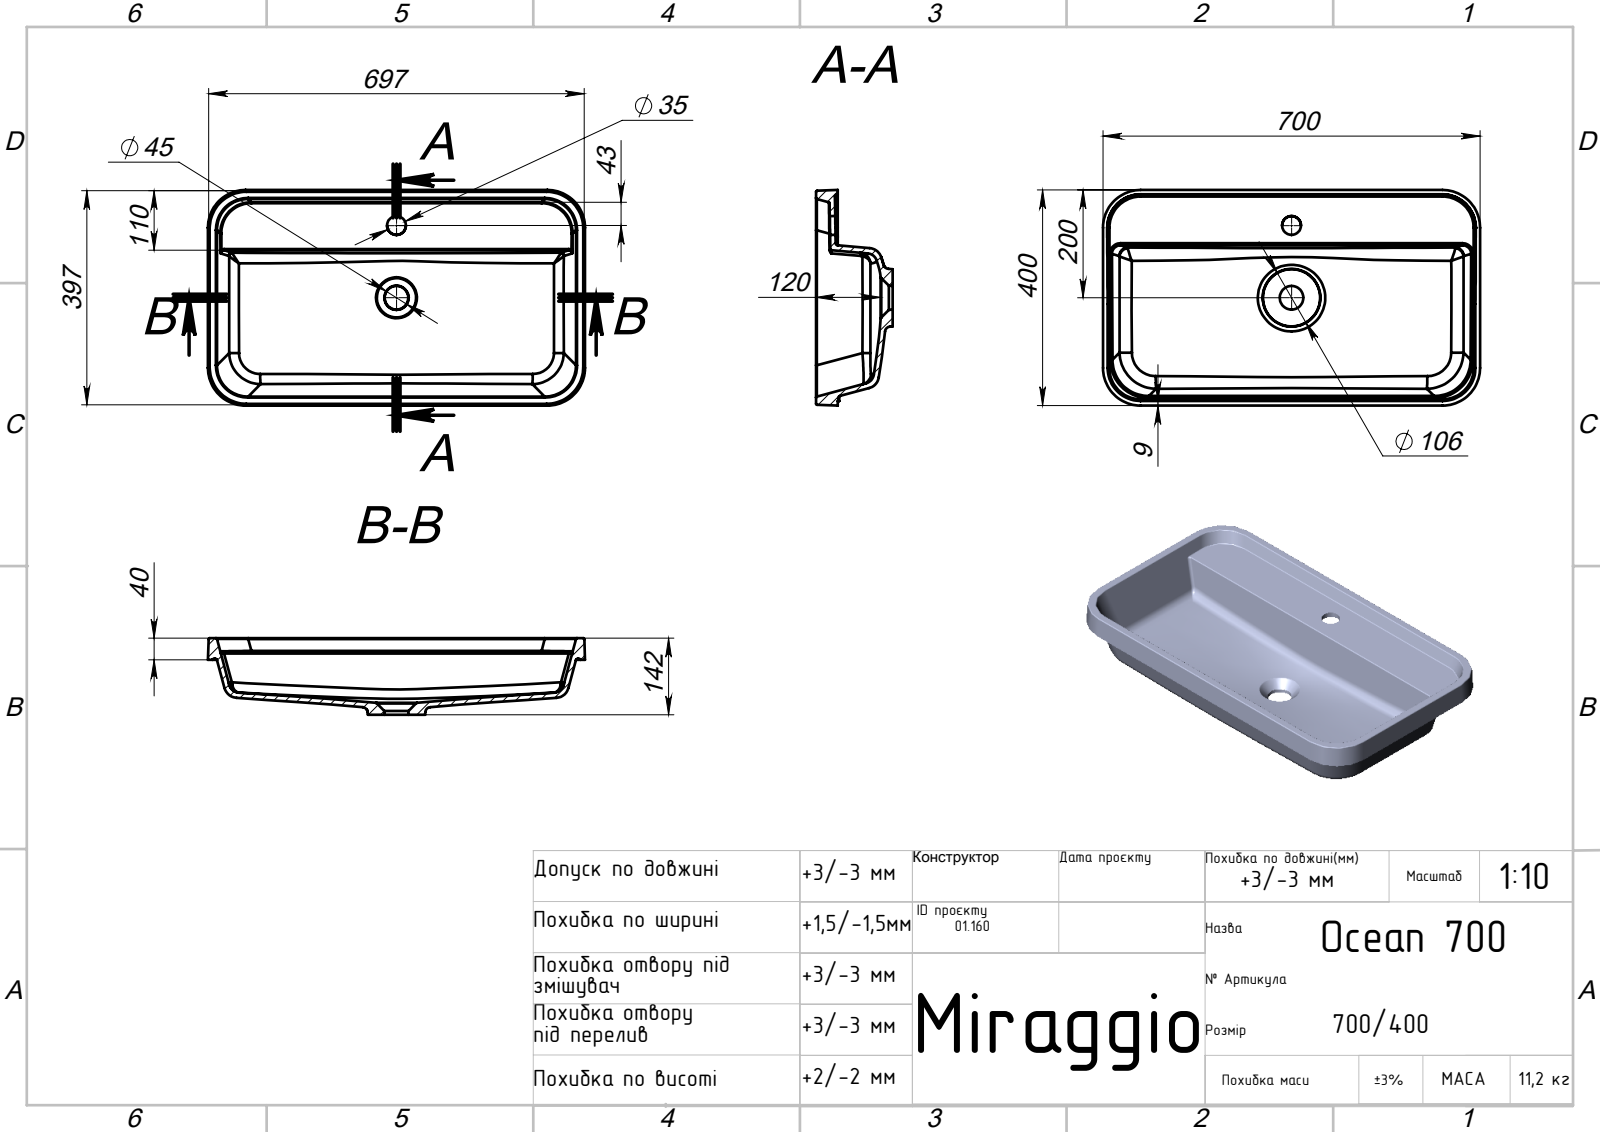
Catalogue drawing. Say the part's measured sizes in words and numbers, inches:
The part is named "Ocean 700". Its 3-D file was written by "SolidWorks 2020 (AUTOMOTIVE_DESIGN)". It is 1 solid with 121 faces: 22 planar, 42 cylindrical and 57 other. Overall it measures 27.559 by 15.748 by 5.591 inches. Its volume is 291.3 cubic inches and its surface area 1 356 square inches. Round holes: 1 of diameter 1.378. Partial cylindrical surfaces (rounded edges, fillets, slot ends): 16 of radius 0.197, 6 of radius 2.756, 4 of radius 0.079, 4 of radius 2.362, 4 of radius 2.441, 3 of radius 0.039, 2 of radius 0.236, 2 of radius 0.63. The main face-to-face distances are 0.394, 0.393, 0.197, 0.591, 4.016, 4.213, 4.606, 5.591, 1.575, 1.378.
